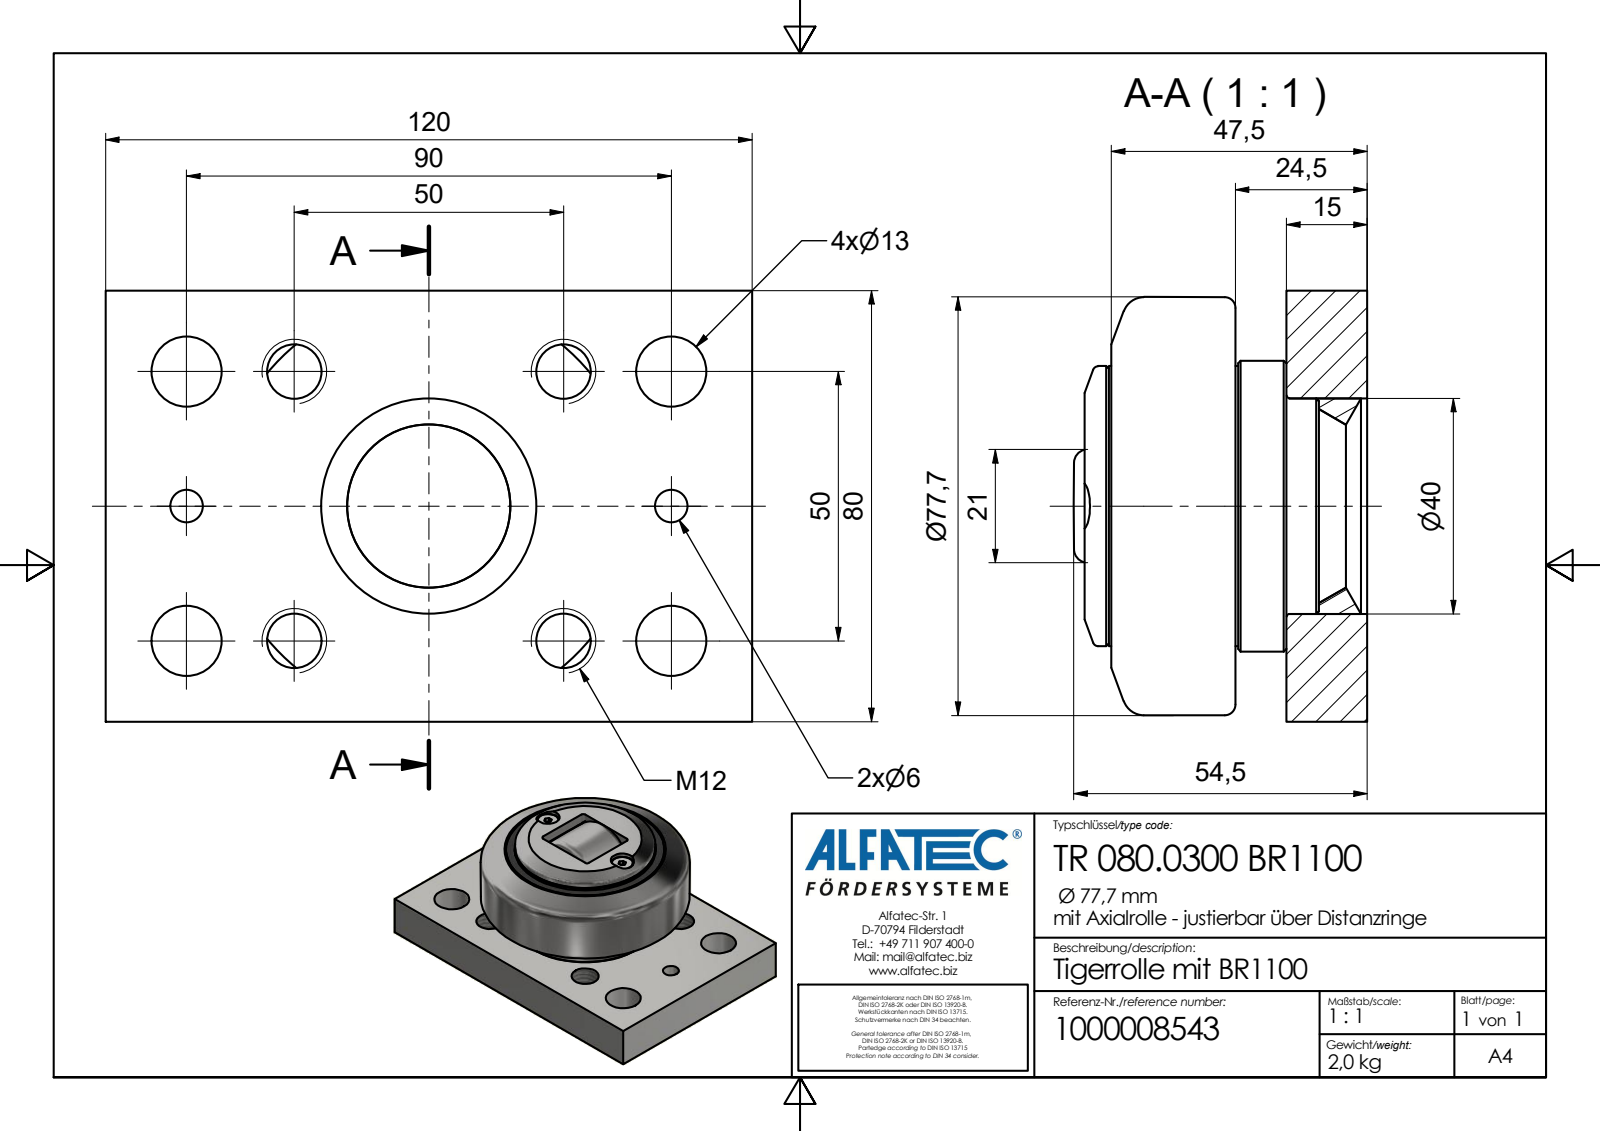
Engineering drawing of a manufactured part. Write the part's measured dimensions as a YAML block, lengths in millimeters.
part_name: "TR 080.0300 BR1100_Kontur"
step_written_by: "Autodesk Inventor 2020 (AP242_MANAGED_MODEL_BASED_3D_ENGINEERING_MIM_LF)"
units: millimeters
bodies: {solids: 1, faces: 105, planar: 46, cylindrical: 38, other: 21}
overall_size: [120, 80, 54.5]
volume: 262101
surface_area: 43473
round_holes:
  - {diameter: 10.11, count: 4}
  - {diameter: 13, count: 4}
  - {diameter: 4.5, count: 2}
  - {diameter: 6, count: 2}
  - {diameter: 8.6, count: 2}
  - {diameter: 40, count: 1}
  - {diameter: 46.2, count: 1}
round_bosses_or_shafts:
  - {diameter: 7.8, count: 2}
  - {diameter: 4, count: 2}
  - {diameter: 54, count: 1}
  - {diameter: 52, count: 1}
  - {diameter: 32.8, count: 1}
partial_cylinders:
  - {radius: 1, count: 4}
  - {radius: 8, count: 1}
  - {radius: 9, count: 1}
  - {radius: 10.5, count: 1}
face_to_face_distances: [15, 24.5, 9.5, 80, 120, 48, 0.5, 23.5, 47.5, 32.5]
hole_center_spacings: [50, 20, 25, 25.6, 32.02, 35.36, 35.71, 51.04]
